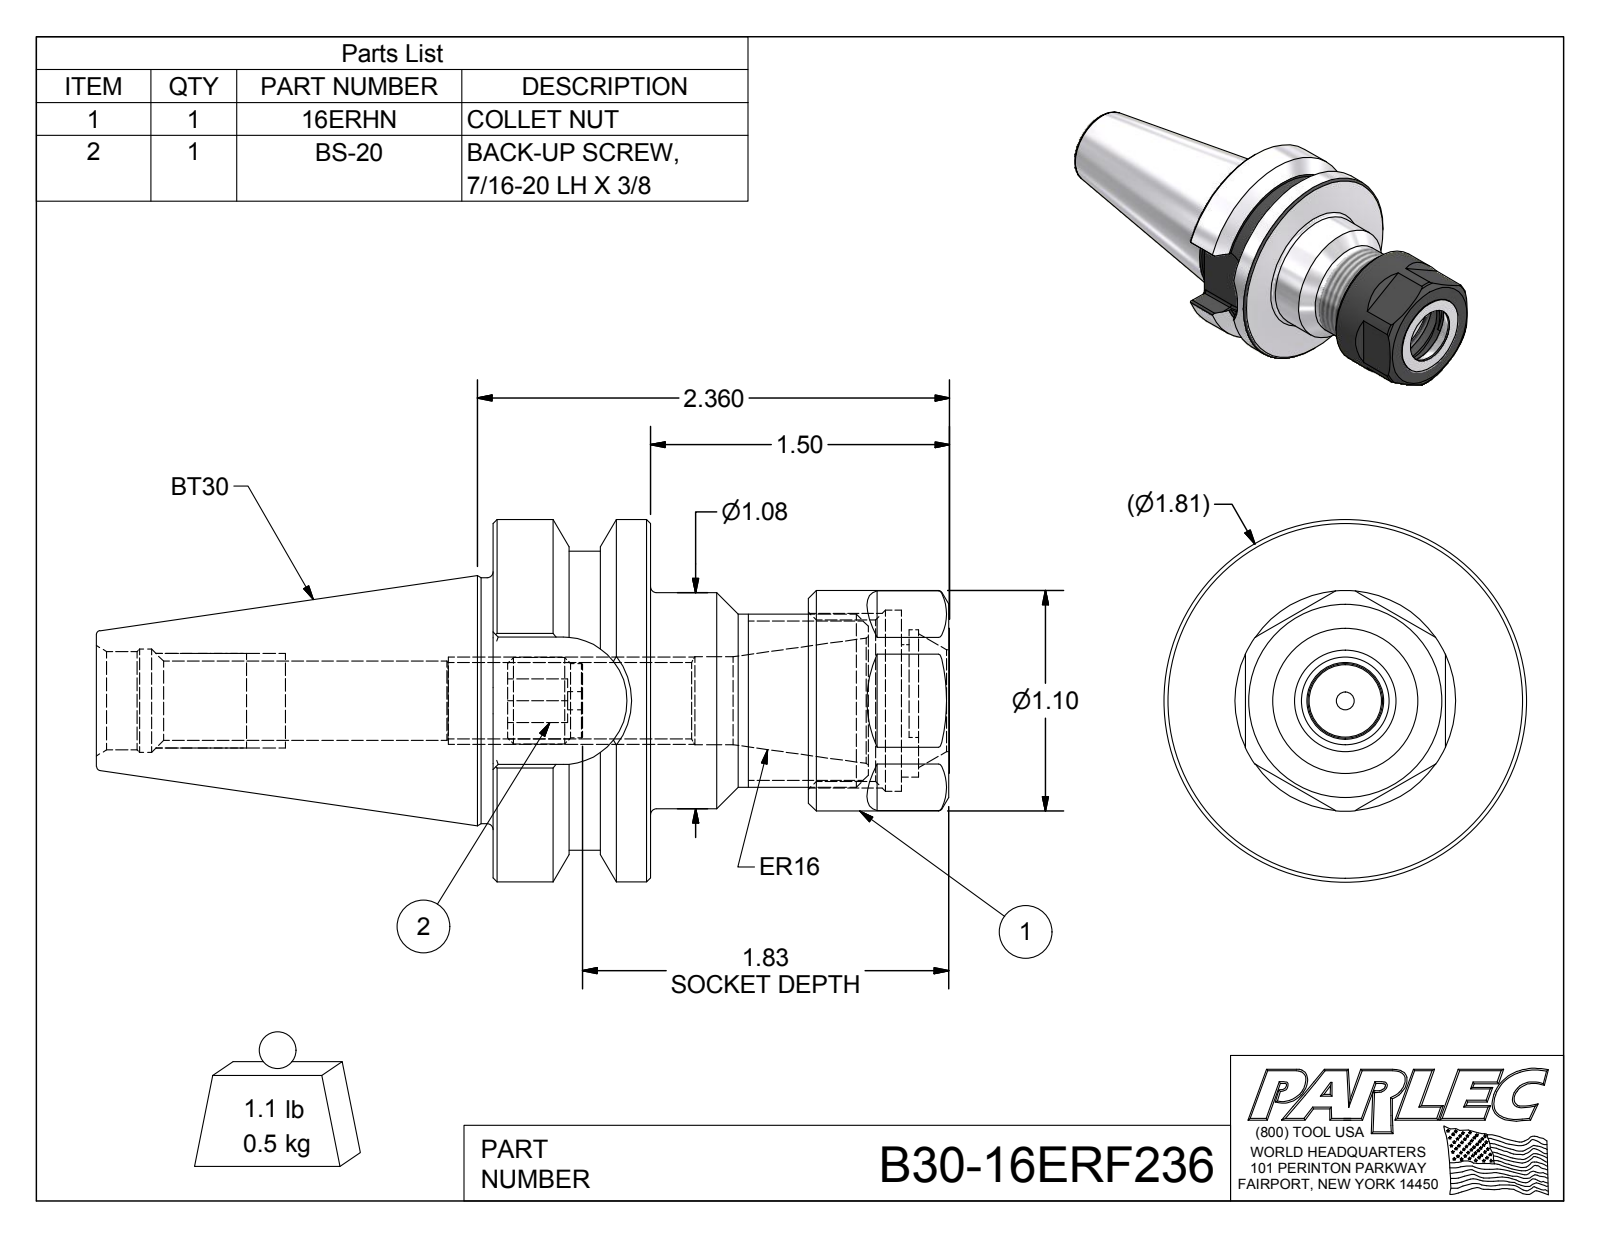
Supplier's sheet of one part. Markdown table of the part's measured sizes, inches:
| quantity | value |
| --- | --- |
| part name | B30-16ER236-1; BS-20; 16ERHN; B30-16ERF236 |
| STEP written by | Autodesk Inventor 2016 (AUTOMOTIVE_DESIGN) |
| units | inches |
| bodies | 3 solids, 122 faces (49 planar, 33 cylindrical, 40 other) |
| overall size | 4.266 × 1.811 × 1.811 |
| volume | 3.762 in³ |
| surface area | 29.69 in² |
| round holes (diameter × count) | 0.09 × 1, 0.383 × 1, 0.398 × 1, 0.44 × 1, 0.488 × 1, 0.493 × 1, 0.517 × 1, 0.67 × 1, 0.807 × 1, 0.906 × 1 |
| round bosses / shafts (diameter × count) | 1.811 × 1, 1.23 × 1, 1.102 × 1, 1.08 × 1, 0.866 × 1, 0.432 × 1, 0.372 × 1 |
| partial cylindrical surfaces (radius × count) | 0.02 × 8, 0.285 × 1, 0.319 × 1, 0.354 × 1, 0.748 × 1 |
| main face-to-face distances | 0.787, 2.282, 1.495, 0.99, 1.283, 0.147, 1.137, 2.057, 1.27, 0.224 |
| hole center spacings | 0.06 |
